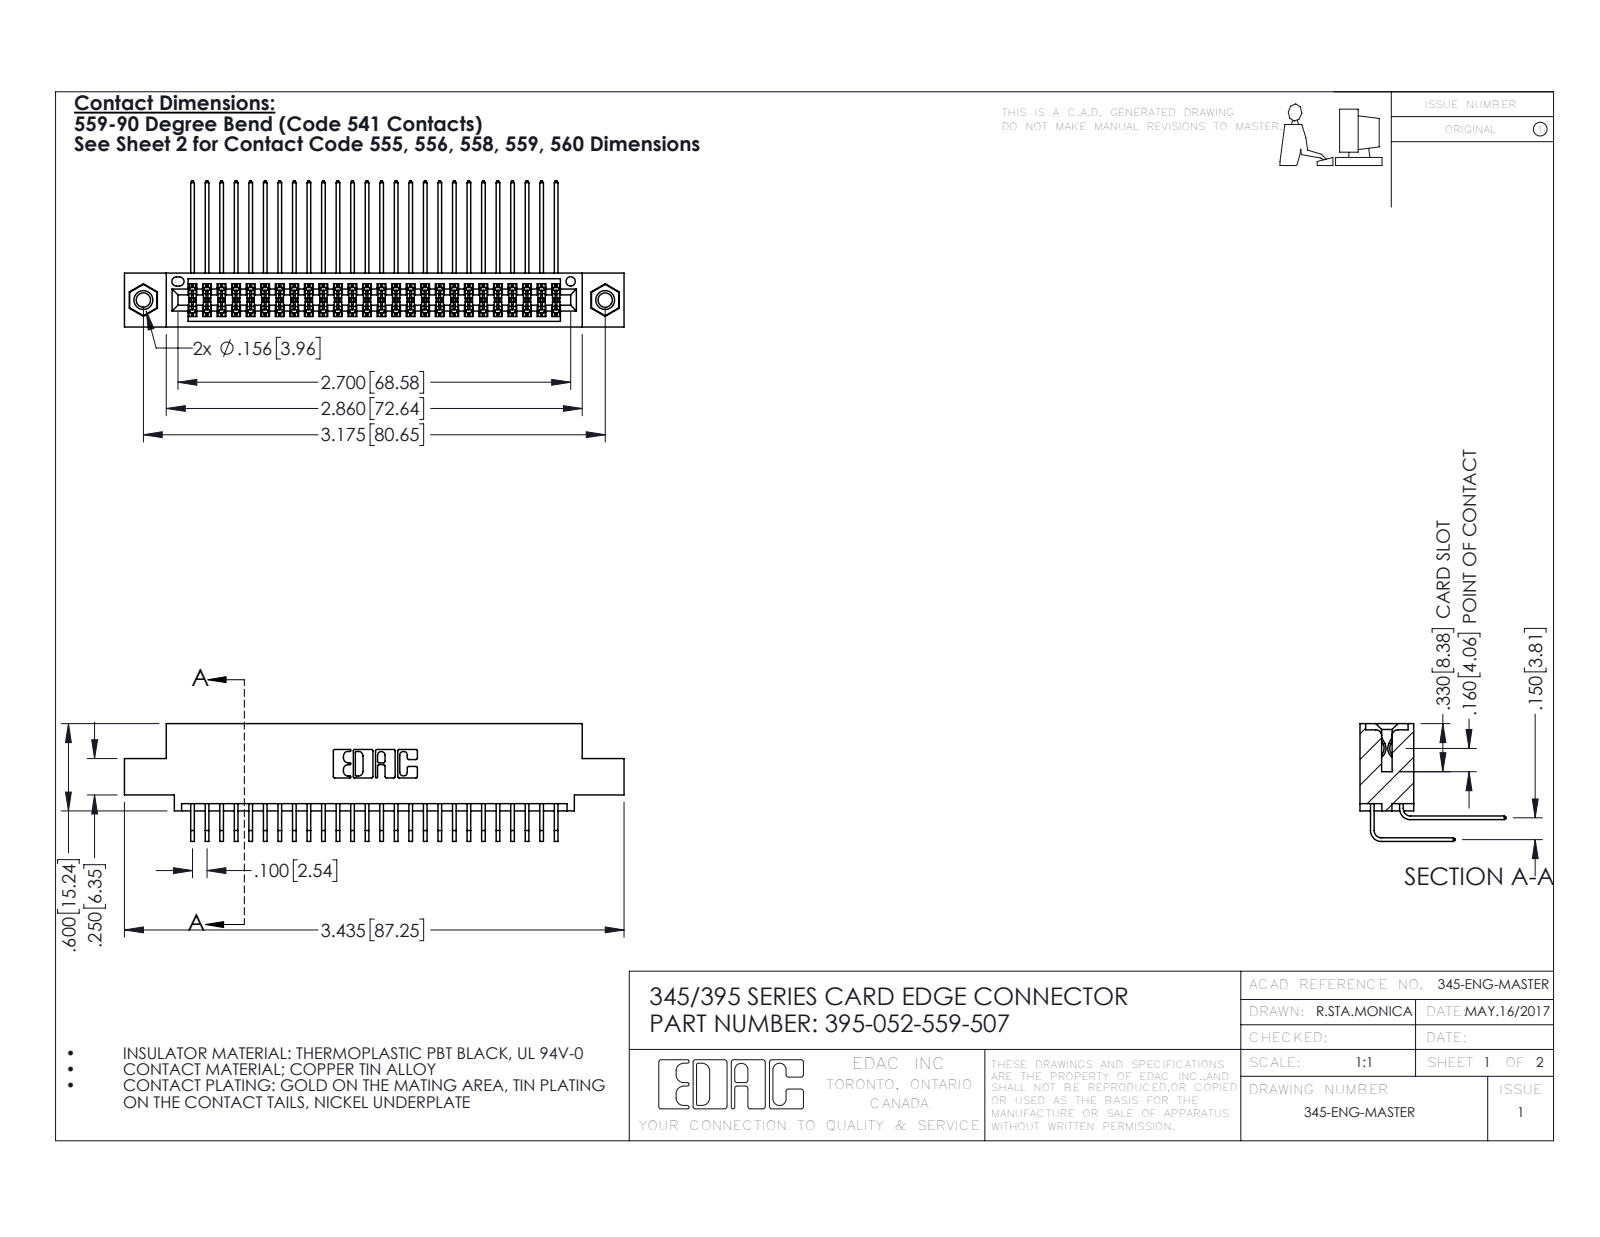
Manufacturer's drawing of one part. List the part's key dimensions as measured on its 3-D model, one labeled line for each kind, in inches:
Part name (STEP PRODUCT): 395-052-559-507; 345-292-001_558 559 Tail - 1; 345-250-001_345-250-005-103; 345 Part_0.110 Offset - 0.156 Dia-TI (+1 more)
STEP written by: SolidWorks 2016 (CONFIG_CONTROL_DESIGN)
Units: inches
Bodies: 55 solids, 2894 faces (1936 planar, 942 cylindrical, 16 other)
Overall size (bounding box): 3.435 × 1.005 × 0.809
Volume: 0.521 in³ · Surface area: 21.46 in²
Round holes (diameter × count): ⌀0.098 ×2, ⌀0.125 ×2, ⌀0.156 ×2, ⌀0.064 ×1
Round bosses / shafts (diameter × count): ⌀0.155 ×2
Partial cylindrical surfaces — rounded edges, fillets, slot ends (radius × count): R0.006 ×79, R0.01 ×22, R0.007 ×6, R0.031 ×6, R0.026 ×3, R0.014 ×2, R0.019 ×2, R0.022 ×2
Main face-to-face distances: 0.072, 0.298, 0.2, 0.37, 0.098, 0.272, 0.025, 0.225, 0.15, 0.175
Hole centre spacings: 0.27, 2.94, 3.175
